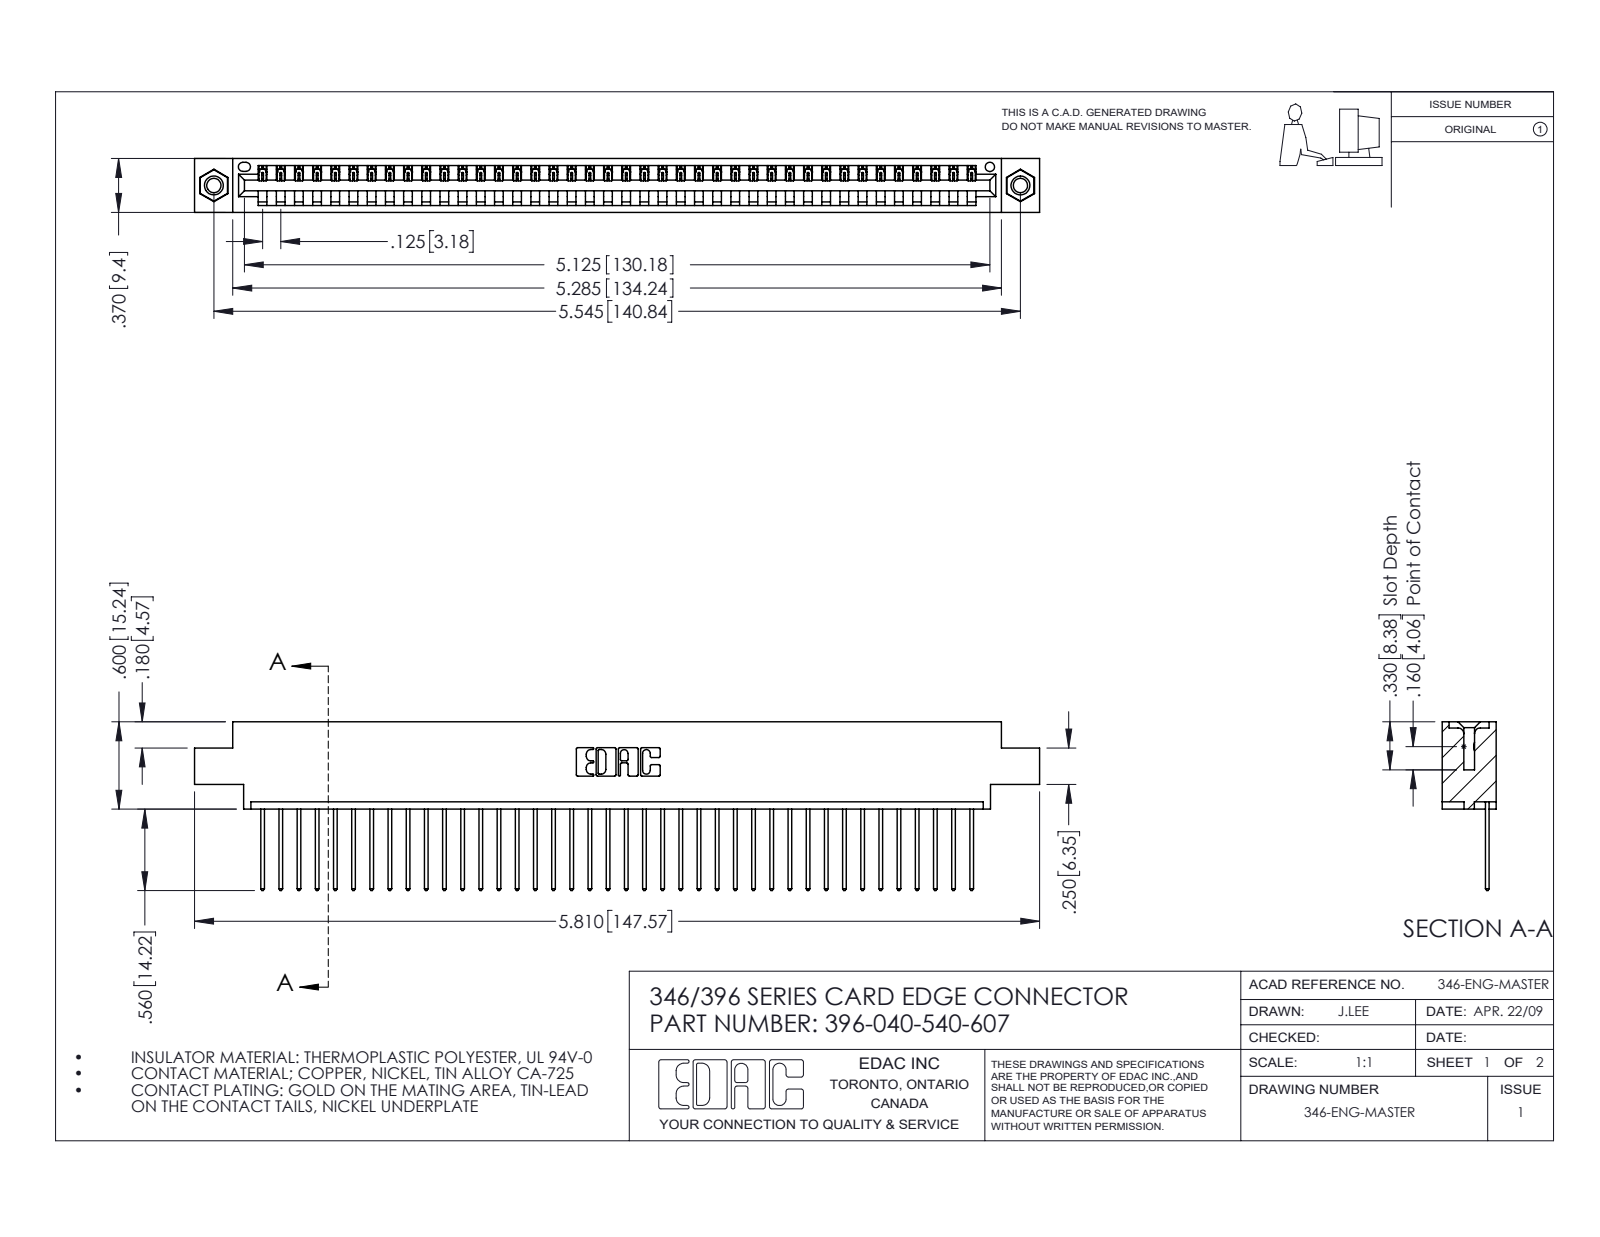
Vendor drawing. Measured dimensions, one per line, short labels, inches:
name: 346 Part_0.170 Offset - 0.156 Dia-TI; 396-040-540-607; 345-250-001_345-250-005-103; 345-292-001_345-293-140
written by: SolidWorks 2016 (CONFIG_CONTROL_DESIGN)
unit: in
bodies: 43 solids, 2506 faces (1712 planar, 778 cylindrical, 16 other)
size: 5.81 × 1.16 × 0.37
volume: 0.854 in³; area: 28 in²
holes: 2× ⌀0.098, 2× ⌀0.125, 2× ⌀0.156, 1× ⌀0.064
bosses: 2× ⌀0.155
rounds: 80× R0.006, 80× R0.01, 22× R0.01, 6× R0.007, 6× R0.031, 3× R0.026, 2× R0.031, 2× R0.04
face distances: 0.048, 0.322, 0.37, 0.25, 0.072, 0.298, 0.025, 0.222, 0.148, 0.1
hole spacings: 0.246, 5.336, 5.545
